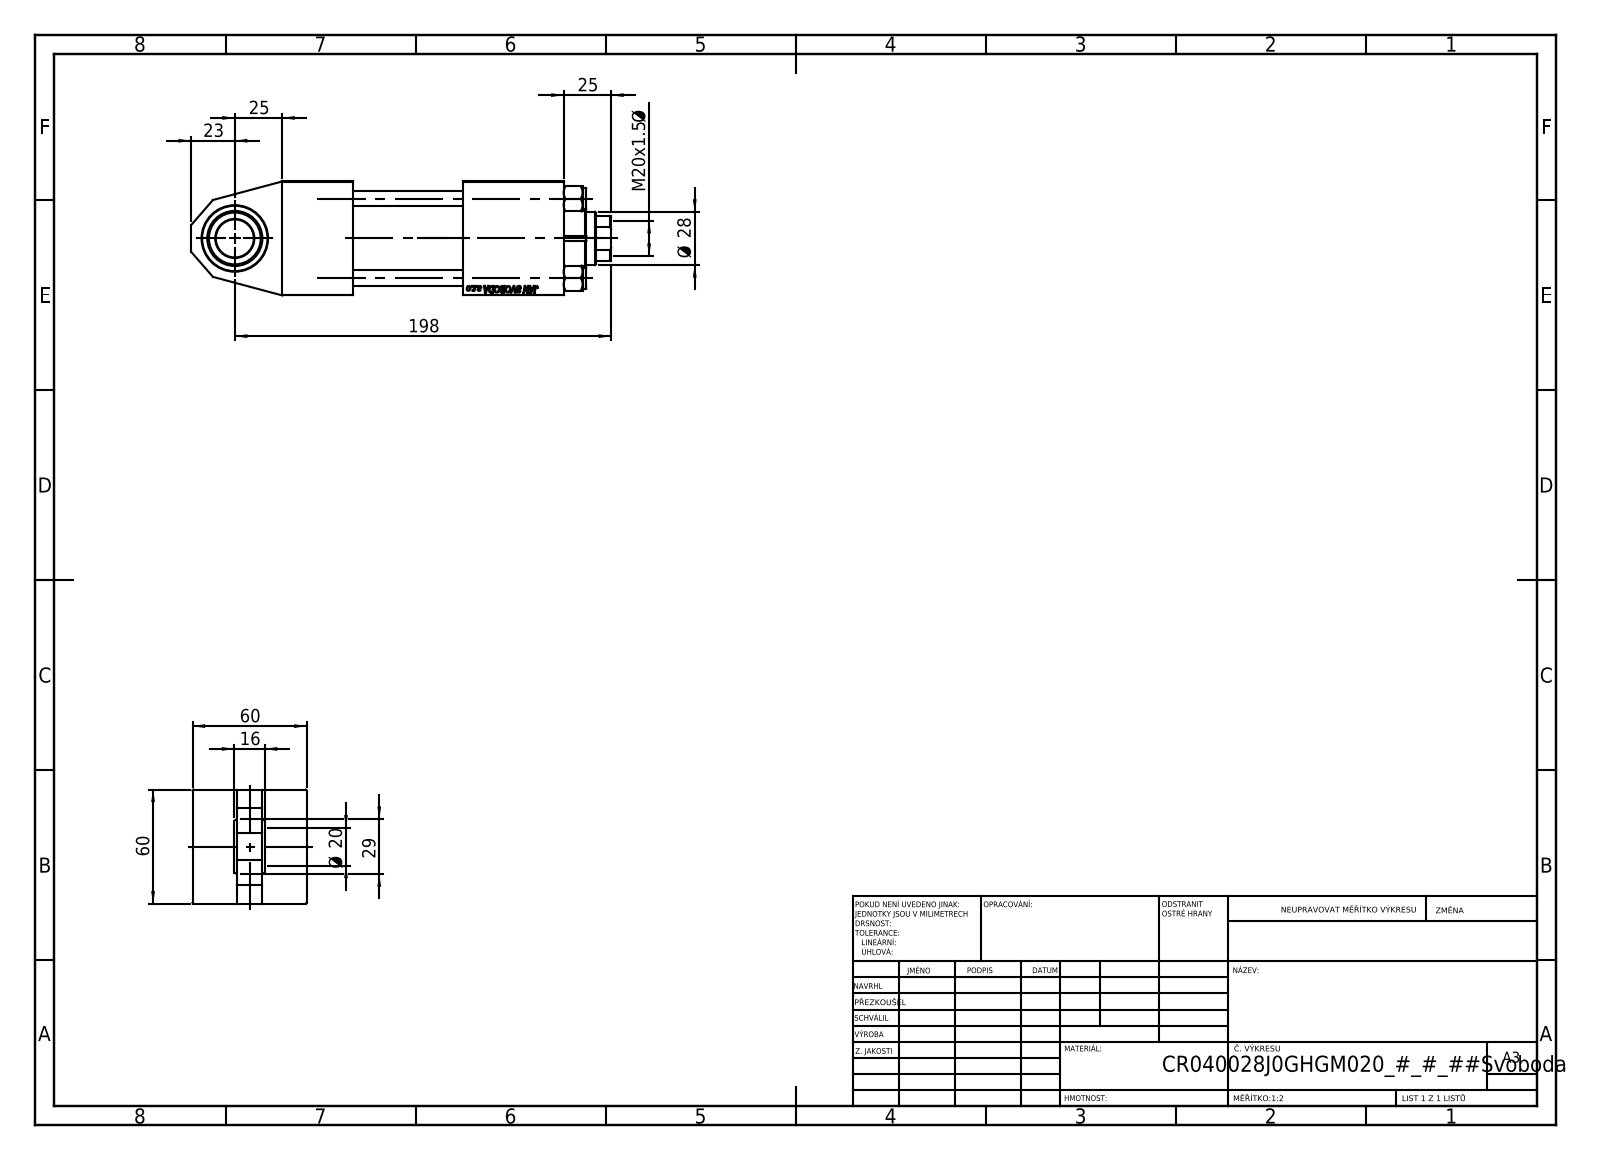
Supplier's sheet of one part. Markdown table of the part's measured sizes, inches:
| quantity | value |
| --- | --- |
| part name | NUT_M5_J; V215_VC_A; V215CR_J_Body; V215CR_TYCINKA_J (+2 more) |
| STEP written by | SolidWorks 2019 (CONFIG_CONTROL_DESIGN) |
| units | inches |
| bodies | 12 solids, 1145 faces (516 planar, 89 cylindrical, 540 other) |
| overall size | 8.701 × 2.362 × 2.362 |
| volume | 27.51 in³ |
| surface area | 187.2 in² |
| round holes (diameter × count) | 0.315 × 4, 0.098 × 2, 0.276 × 2, 0.656 × 2, 0.945 × 2, 0.728 × 1, 0.787 × 1, 1.102 × 1, 1.22 × 1, 1.378 × 1, 1.575 × 1, 1.772 × 1 |
| round bosses / shafts (diameter × count) | 0.433 × 4, 1.811 × 1, 1.654 × 1 |
| partial cylindrical surfaces (radius × count) | 0.531 × 1 |
| main face-to-face distances | 2.362, 1.437, 0.925, 1.457, 2.087, 2.283, 3.74, 5.827, 4.37, 0.512 |
| hole center spacings | 0.821, 1.161, 1.642, 1.832, 0.817, 2.322, 1.634, 1.713 |
